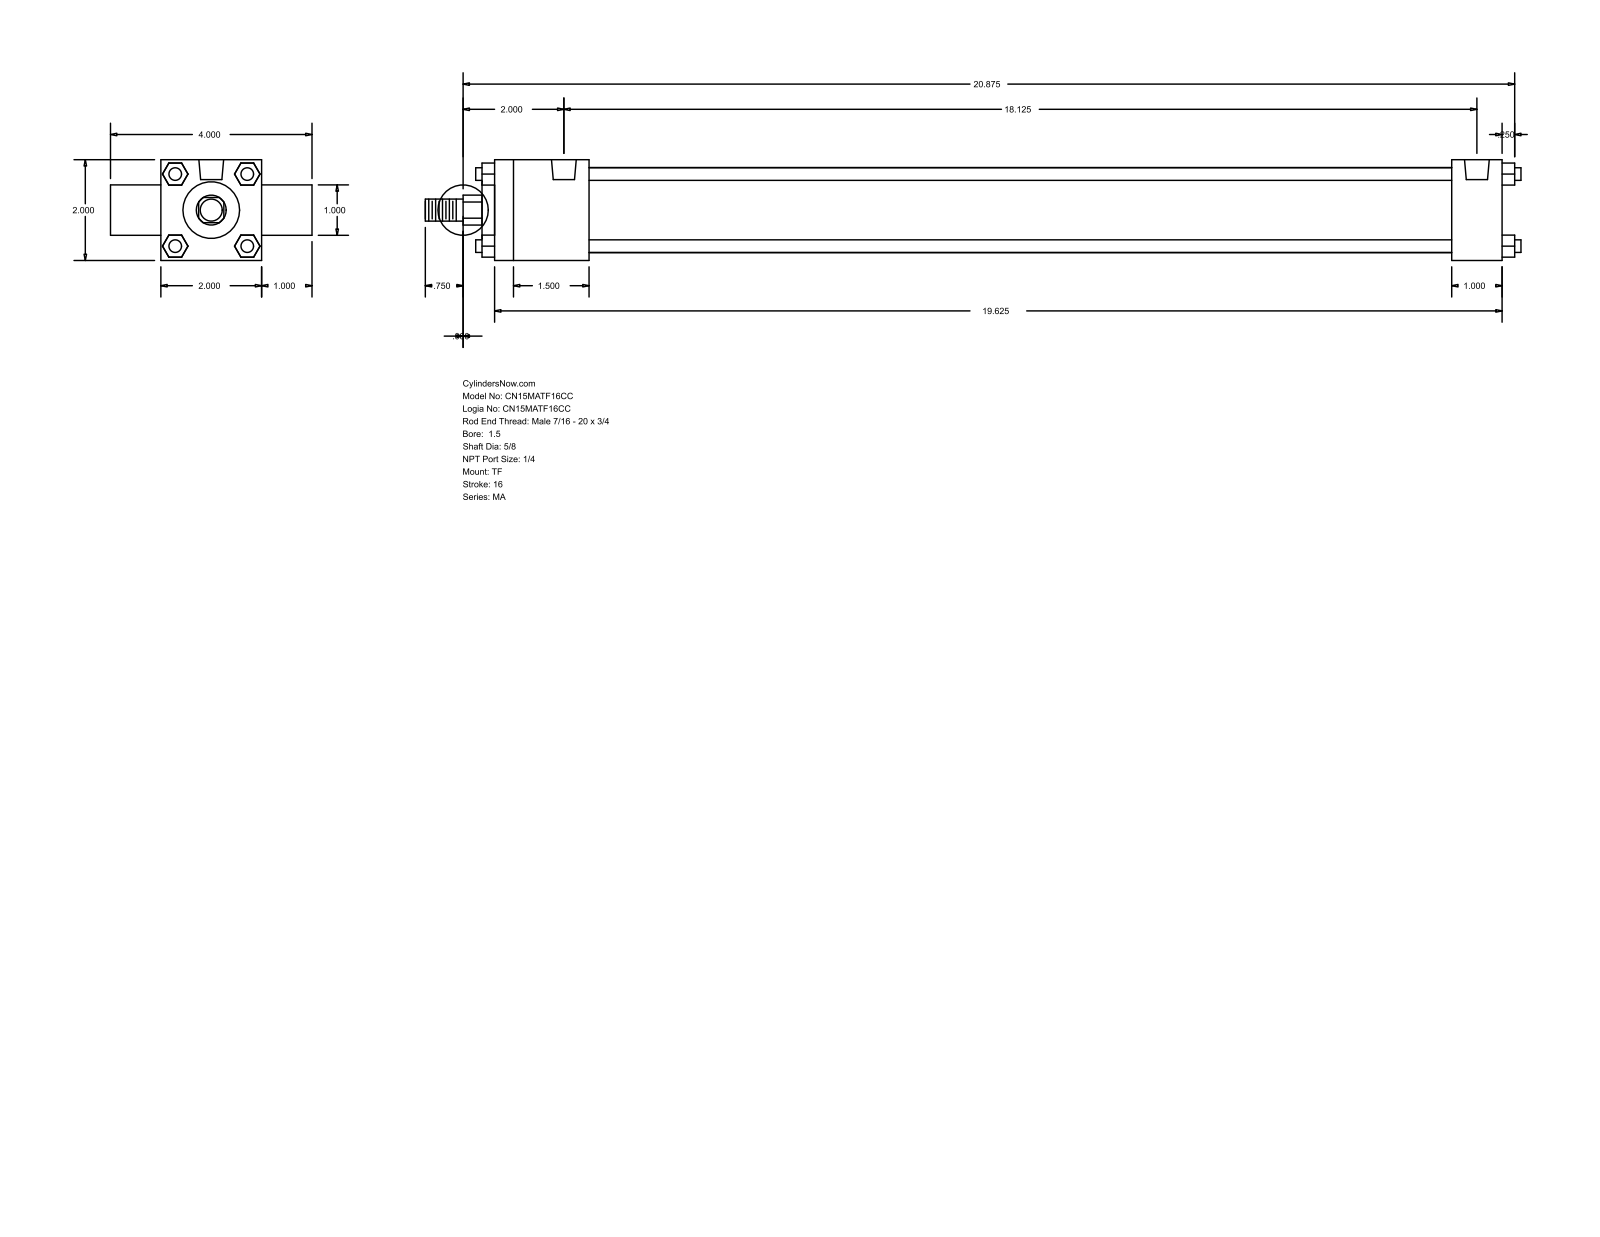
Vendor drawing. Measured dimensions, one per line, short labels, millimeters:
name: MA_TF__0150_0.625
written by: GSSL Pune (CONFIG_CONTROL_DESIGN)
unit: mm
bodies: 0 solids, 120 faces (92 planar, 28 cylindrical, 0 other)
size: 552.45 × 101.6 × 50.8
holes: 3× ⌀7.94, 2× ⌀12.49
bosses: 4× ⌀6.35, 1× ⌀42.93, 1× ⌀28.57, 1× ⌀25.4, 1× ⌀15.88, 1× ⌀11.11
rounds: 1× R7.54
face distances: 50.8, 25.4, 508, 6.35, 514.35, 76.2, 47.62, 482.6, 434.98, 460.38
hole spacings: 460.38
